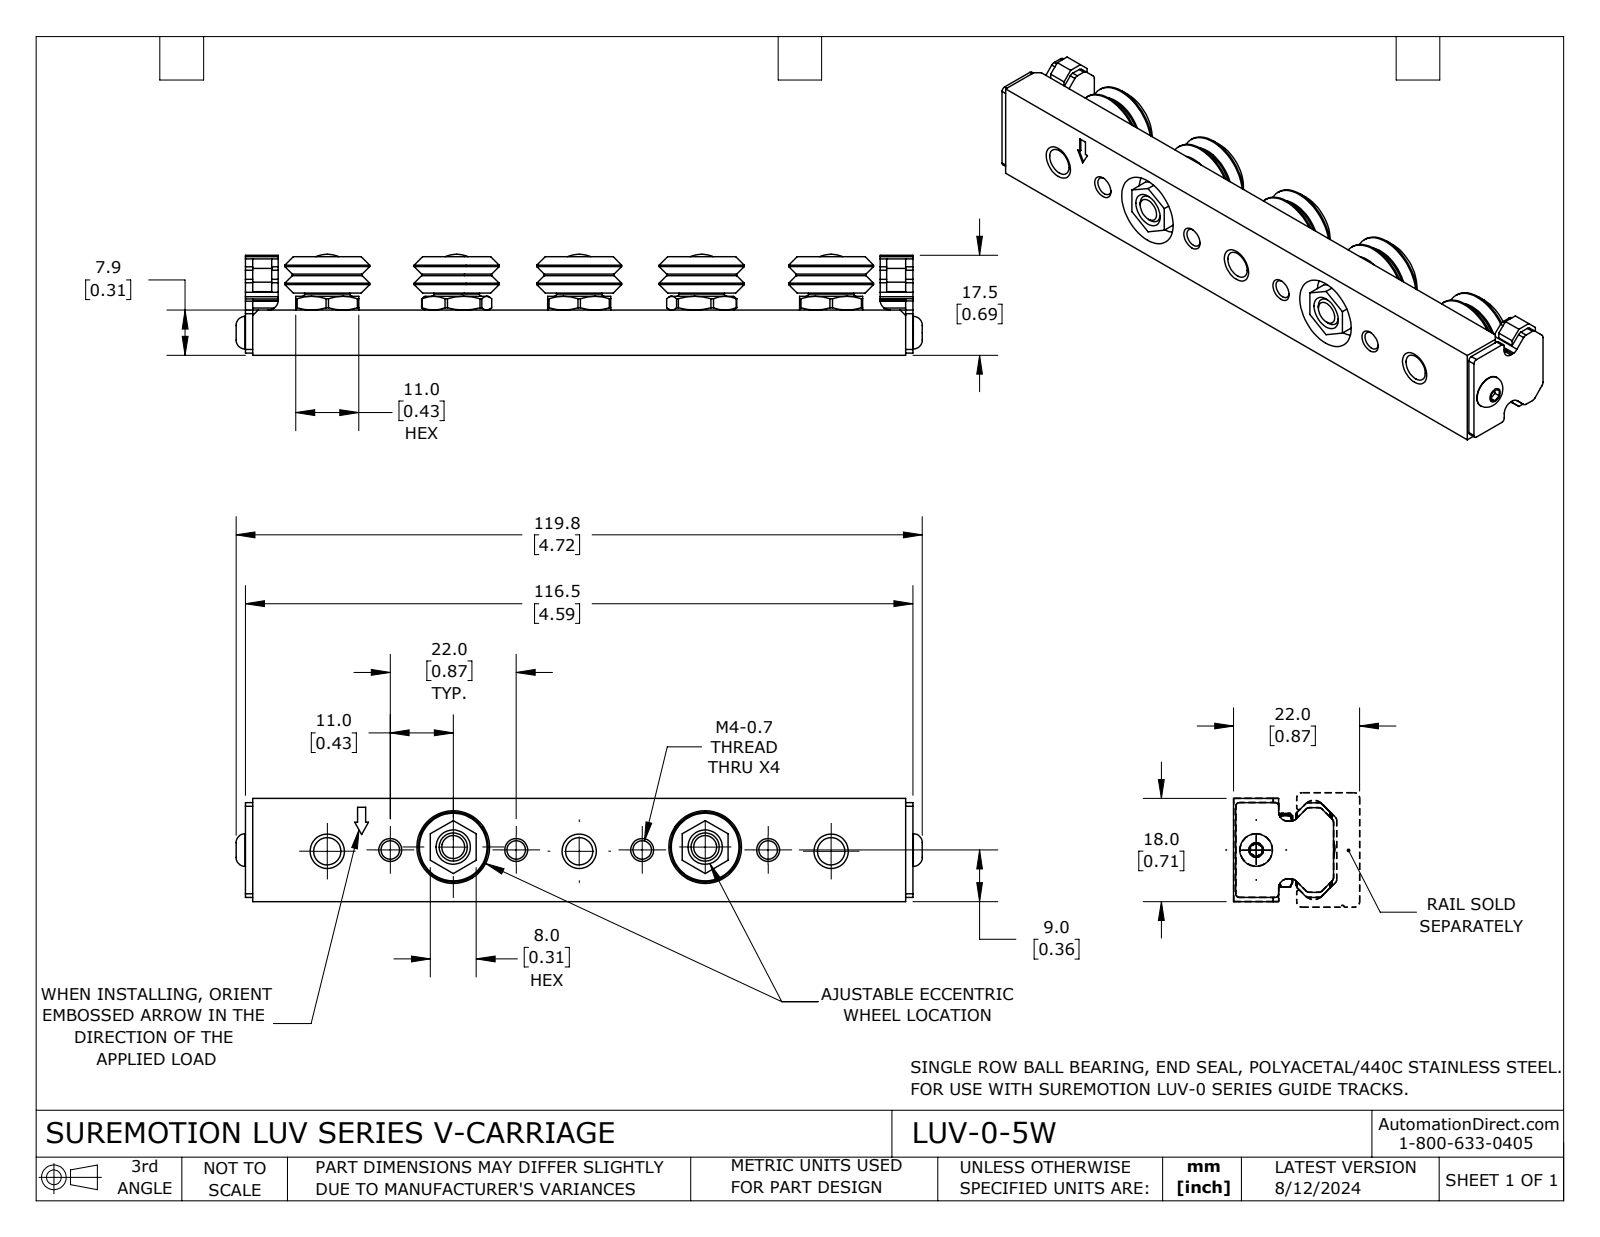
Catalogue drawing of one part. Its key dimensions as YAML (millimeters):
part_name: "LUV-0-5W"
step_written_by: "SolidWorks 2023 (CONFIG_CONTROL_DESIGN)"
units: millimeters
bodies: {solids: 10, faces: 962, planar: 265, cylindrical: 292, other: 405}
overall_size: [119.83, 18.01, 17.63]
volume: 22833
surface_area: 15483
round_holes:
  - {diameter: 4, count: 5}
  - {diameter: 9.18, count: 5}
  - {diameter: 9.44, count: 5}
  - {diameter: 3.24, count: 4}
  - {diameter: 4.92, count: 4}
  - {diameter: 5.63, count: 2}
  - {diameter: 12.7, count: 2}
  - {diameter: 2.46, count: 1}
  - {diameter: 4.92, count: 1}
round_bosses_or_shafts:
  - {diameter: 14.83, count: 5}
  - {diameter: 7.92, count: 5}
  - {diameter: 3.99, count: 5}
  - {diameter: 6.22, count: 4}
  - {diameter: 6.48, count: 3}
  - {diameter: 6, count: 3}
  - {diameter: 4.5, count: 3}
  - {diameter: 11.81, count: 2}
partial_cylinders:
  - {radius: 0.38, count: 12}
  - {radius: 0.84, count: 6}
  - {radius: 6.22, count: 5}
  - {radius: 0.64, count: 4}
  - {radius: 1.6, count: 4}
  - {radius: 1.78, count: 2}
face_to_face_distances: [7.87, 18, 1.27, 115.27, 6.35, 2.72, 5.15, 2.97, 5.69, 10.84]
hole_center_spacings: [11, 32.99, 43.99, 54.99, 22, 0.62, 10.41, 11.01]
